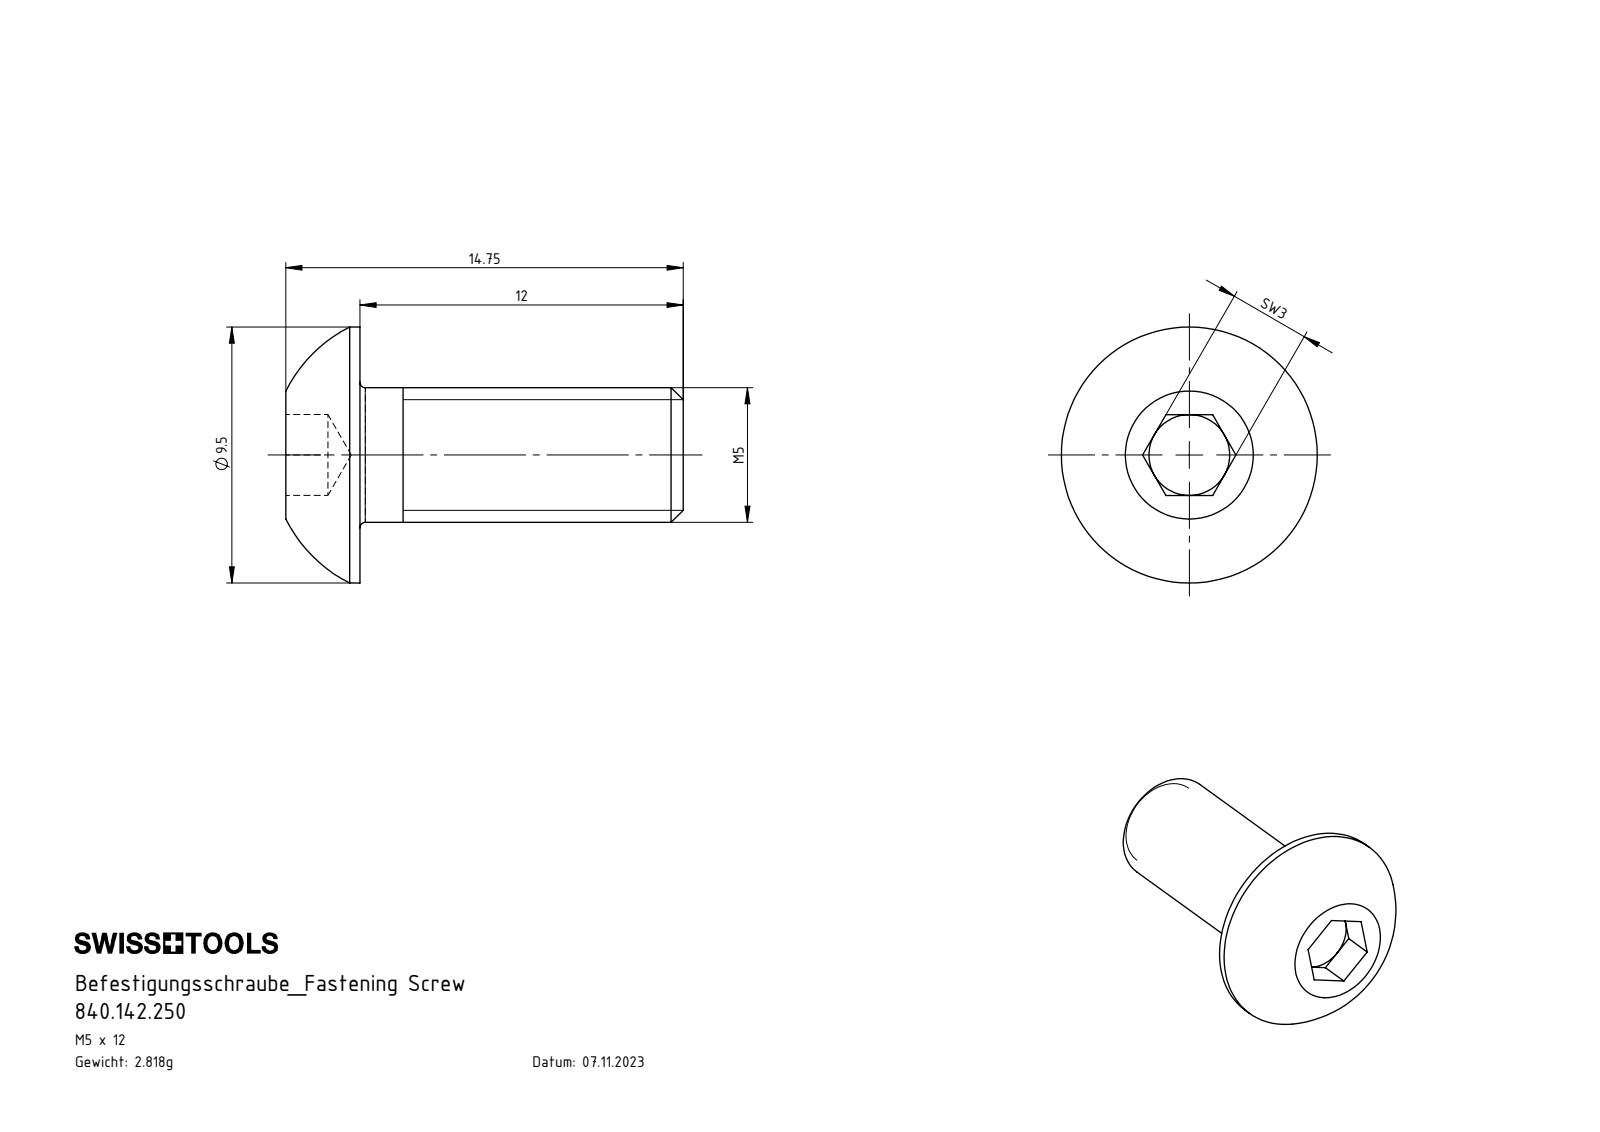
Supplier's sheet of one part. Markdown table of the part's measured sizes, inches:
| quantity | value |
| --- | --- |
| part name | 840.142.250 |
| STEP written by | SolidWorks 2022 (AUTOMOTIVE_DESIGN) |
| units | inches |
| bodies | 1 solid, 27 faces (15 planar, 4 cylindrical, 8 other) |
| overall size | 0.581 × 0.374 × 0.374 |
| volume | 0.022 in³ |
| surface area | 0.587 in² |
| round bosses / shafts (diameter × count) | 0.374 × 1, 0.197 × 1 |
| main face-to-face distances | 0.472, 0.108, 0.581, 0.118, 0.061, 0.047, 0.519 |
